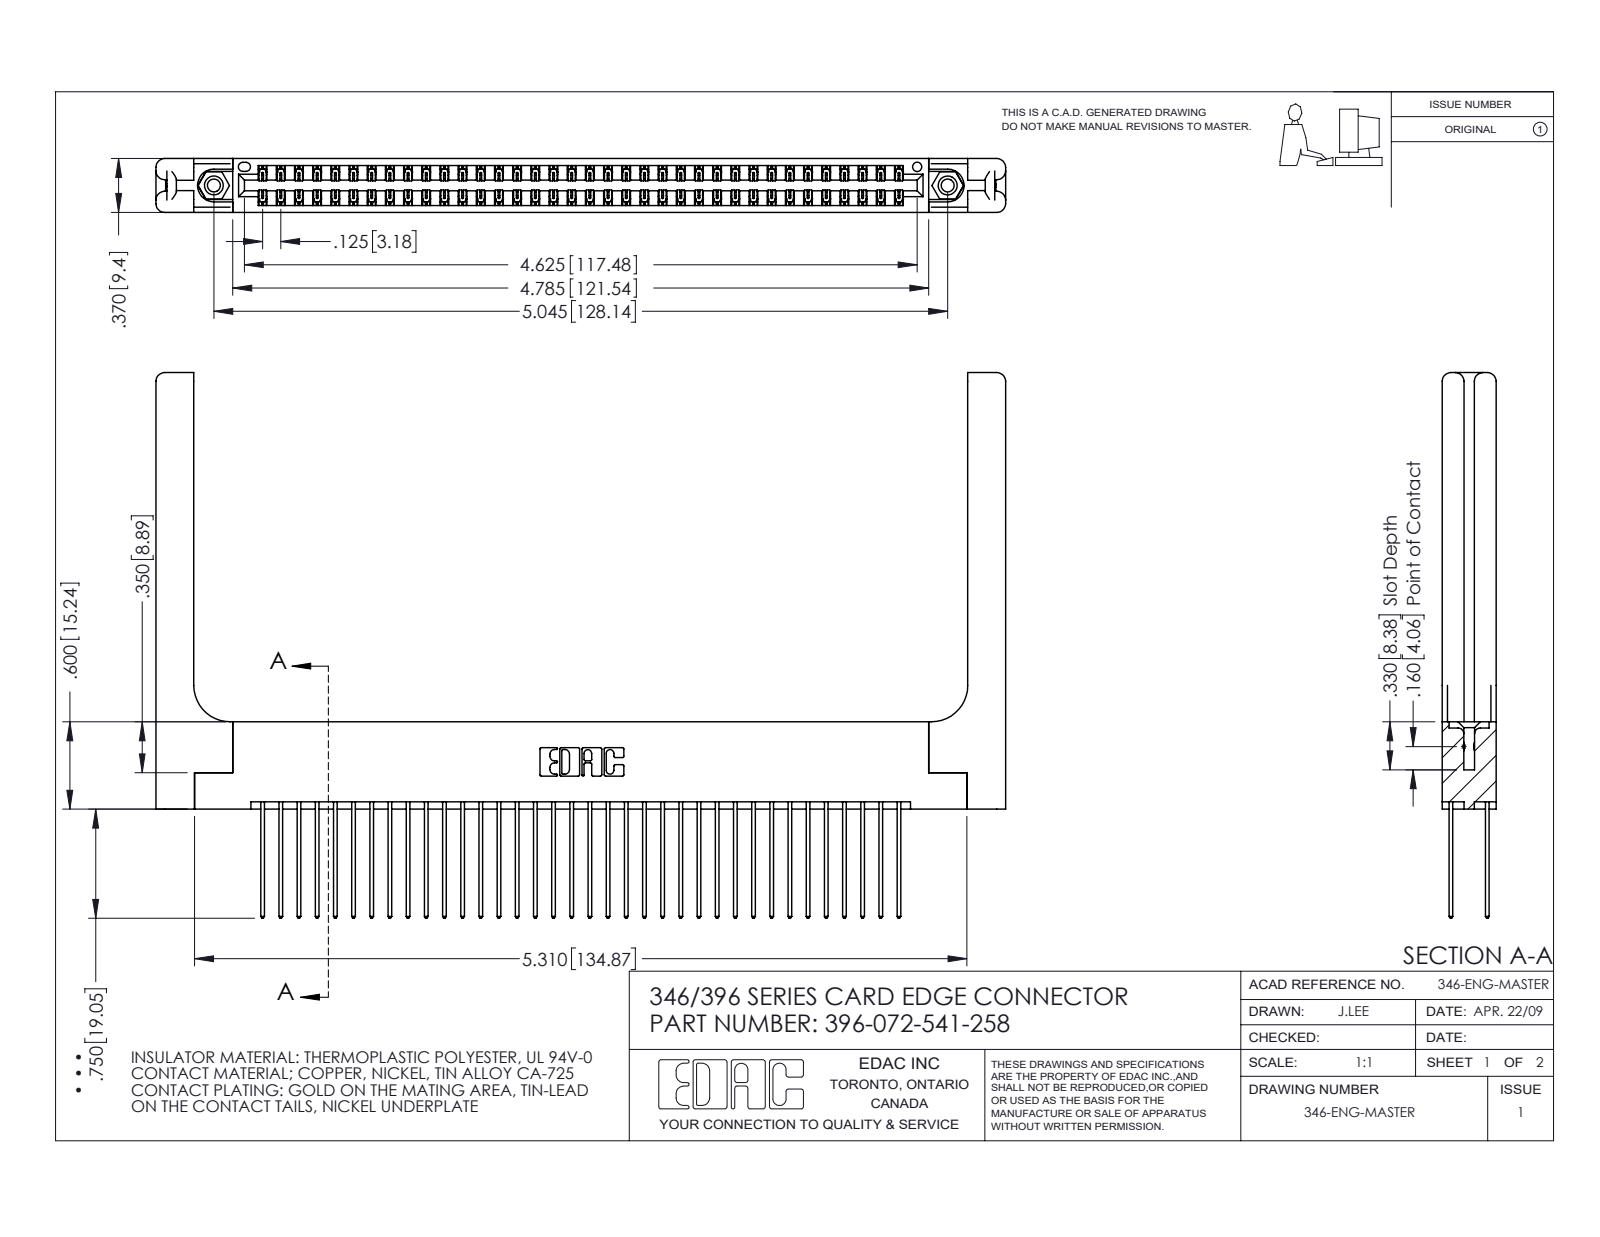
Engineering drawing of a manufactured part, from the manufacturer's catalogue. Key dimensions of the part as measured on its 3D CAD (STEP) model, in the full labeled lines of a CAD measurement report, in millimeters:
Part name (STEP PRODUCT): 396-072-541-258; 345-250-001_345-250-001-102; 345-292-001_345-293-141; 346 Part_Flush Mounting Lugs - 0.156 Dia-TH (+1 more)
STEP written by: SolidWorks 2016 (CONFIG_CONTROL_DESIGN)
Units: millimetres
Bodies: 77 solids, 4122 faces (2744 planar, 1318 cylindrical, 60 other)
Overall size (bounding box): 148.4 × 95.3 × 9.4
Volume: 22 340 mm³ · Surface area: 27 250 mm²
Round holes (diameter × count): ⌀2.3 ×2, ⌀3.2 ×2, ⌀4 ×2, ⌀1.6 ×1
Round bosses / shafts (diameter × count): ⌀3.9 ×2
Partial cylindrical surfaces — rounded edges, fillets, slot ends (radius × count): R0.2 ×108, R0.3 ×72, R0.3 ×22, R1.5 ×16, R0.2 ×6, R0.8 ×6, R0.7 ×3, R0.4 ×2
Main face-to-face distances: 1.2, 8.2, 1.8, 9.4, 6.4, 0.6, 7.6, 3.8, 3.8, 7
Hole centre spacings: 6.2, 122.8, 128.1
